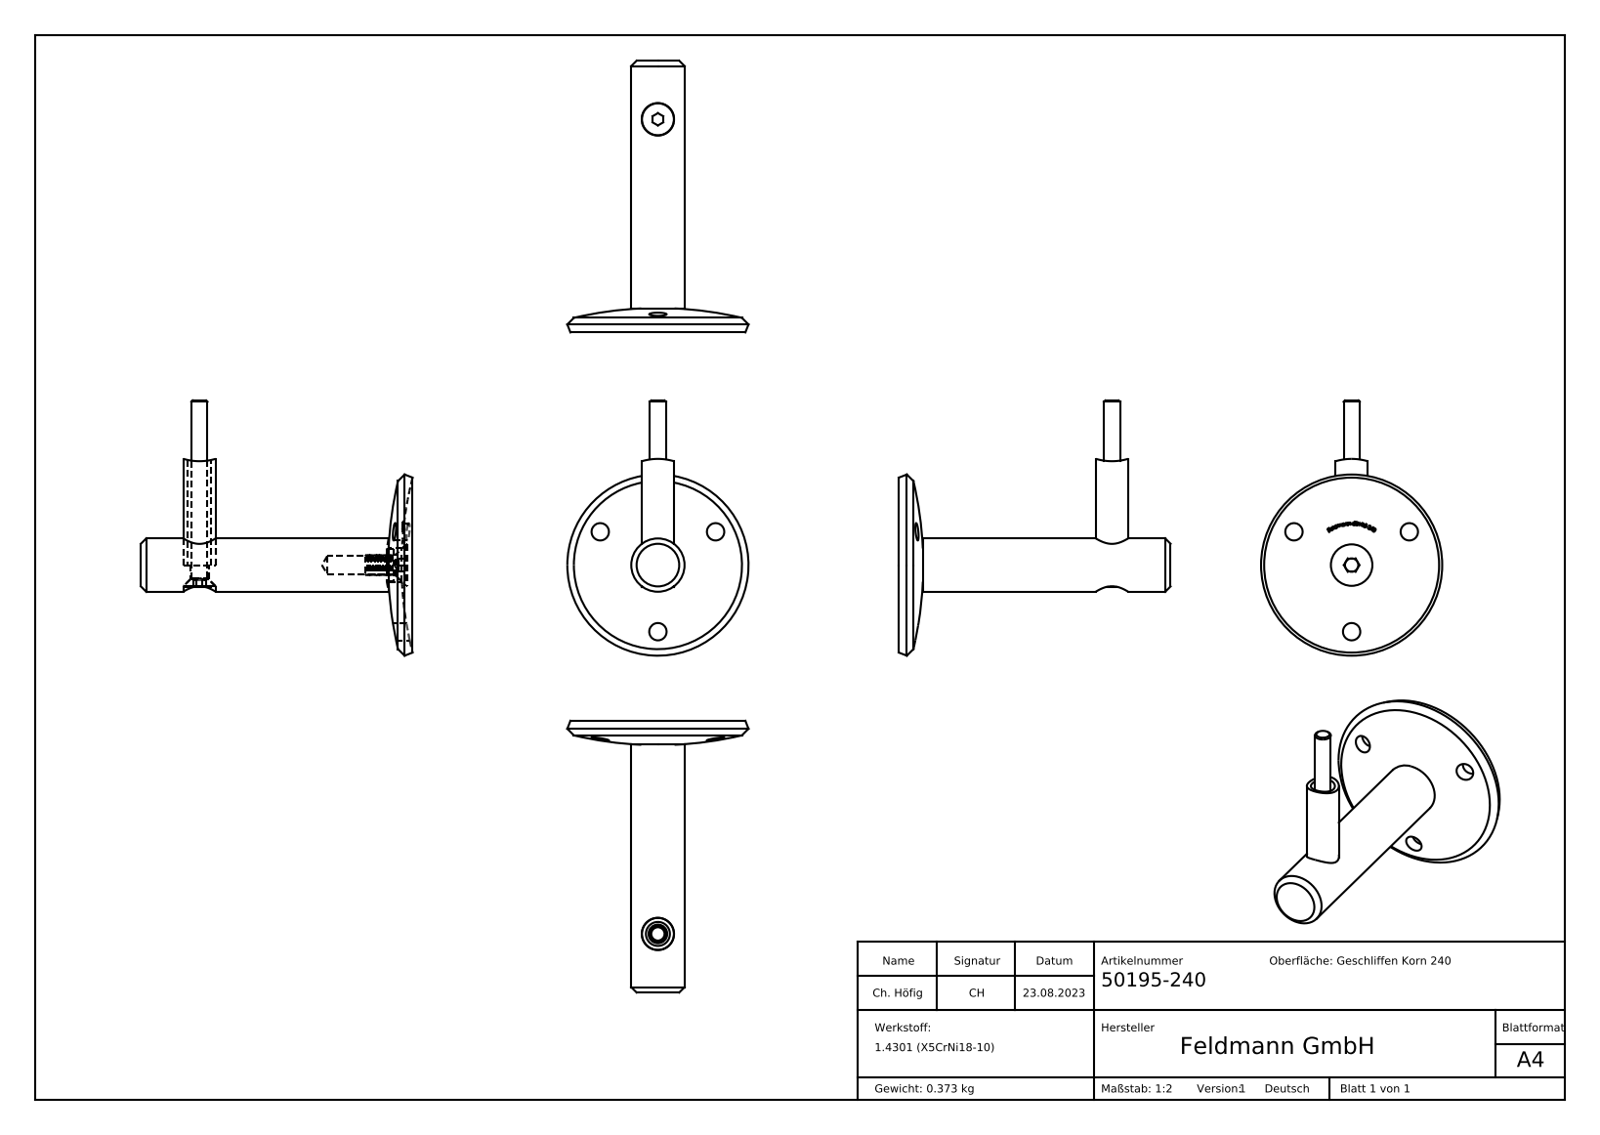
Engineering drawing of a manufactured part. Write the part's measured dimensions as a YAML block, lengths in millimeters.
part_name: "socket countersunk head screw_din_DIN 7991 - M8 x 16 --- 16S; 50195-240 Teil4_50195-240 Teil4; 50195-240 Teil3_50195-240 Teil3; 50195-240 (+2 more)"
step_written_by: "SolidWorks 2018 (CONFIG_CONTROL_DESIGN)"
units: millimeters
bodies: {solids: 5, faces: 302, planar: 124, cylindrical: 26, other: 152}
overall_size: [102, 95.8, 68]
volume: 48100
surface_area: 20775
round_holes:
  - {diameter: 6.5, count: 3}
  - {diameter: 6.8, count: 1}
  - {diameter: 7, count: 1}
  - {diameter: 9, count: 1}
  - {diameter: 12.1, count: 1}
  - {diameter: 12.2, count: 1}
  - {diameter: 12.5, count: 1}
round_bosses_or_shafts:
  - {diameter: 12, count: 2}
  - {diameter: 20, count: 1}
  - {diameter: 15.57, count: 1}
  - {diameter: 8, count: 1}
  - {diameter: 6, count: 1}
partial_cylinders:
  - {radius: 21.2, count: 1}
face_to_face_distances: [100.16, 8.2, 5.16, 95, 16, 10.84, 84.16, 5.02, 2.51, 70]
hole_center_spacings: [25, 43.3]
